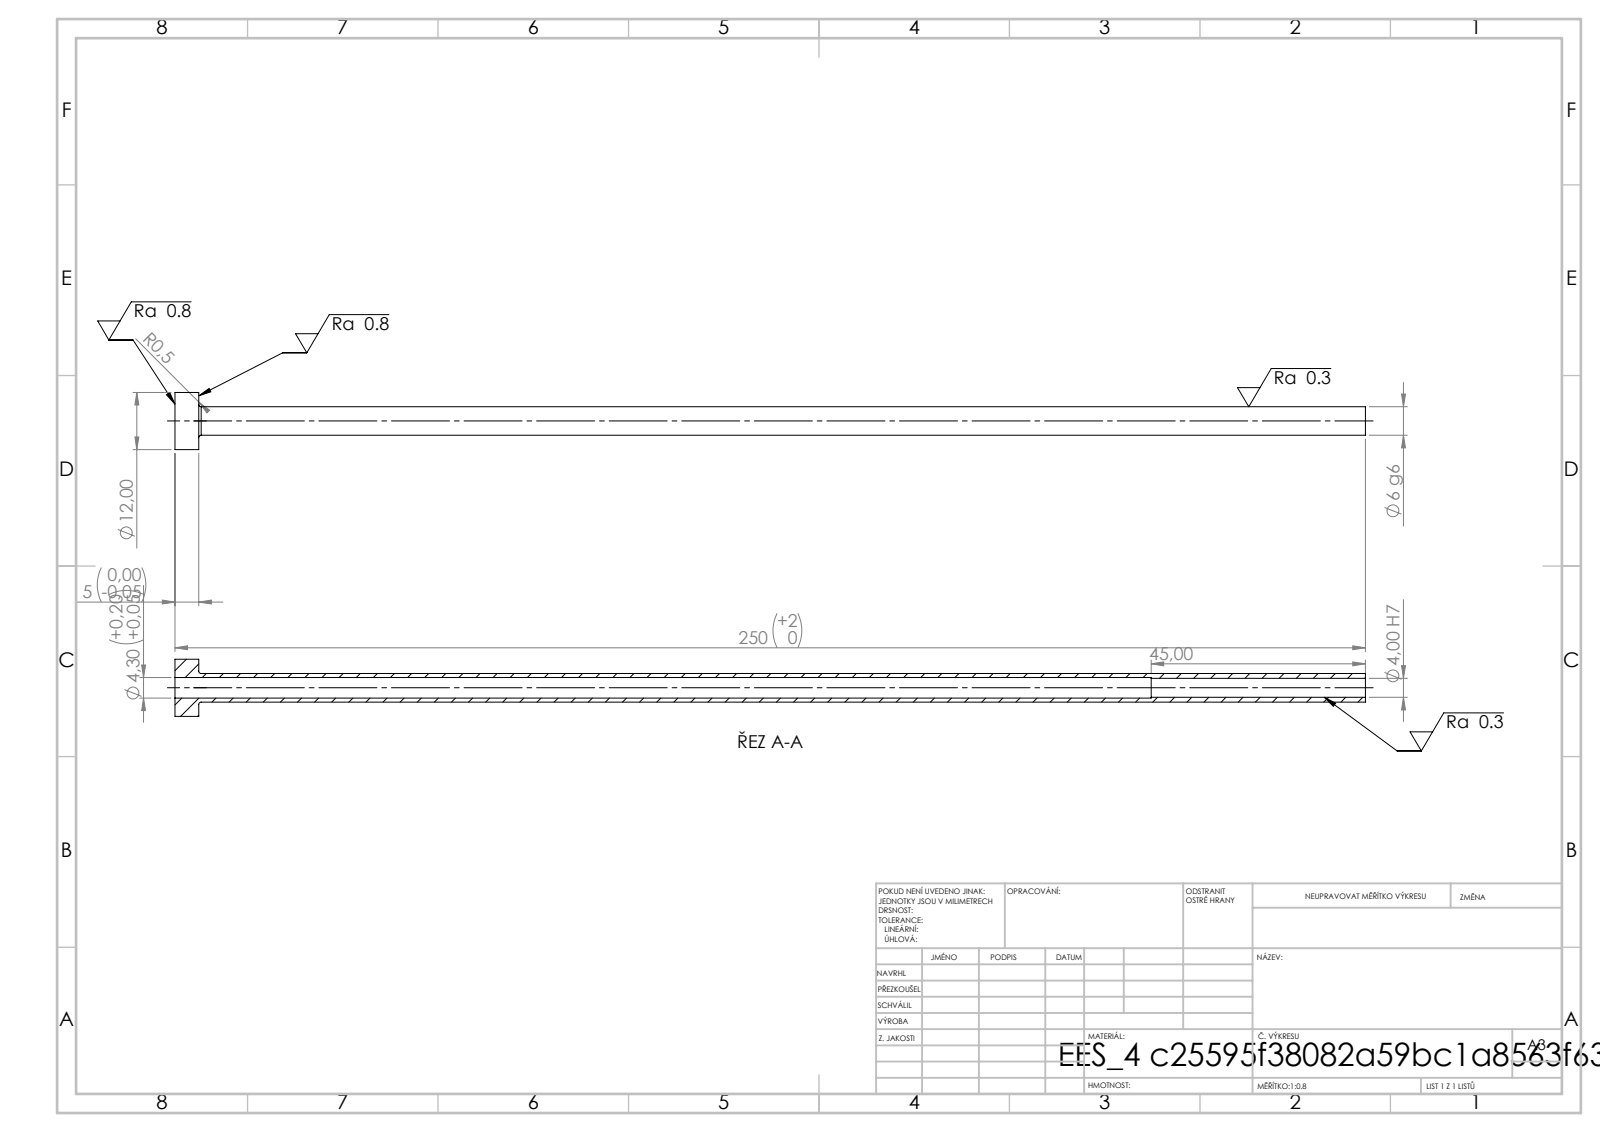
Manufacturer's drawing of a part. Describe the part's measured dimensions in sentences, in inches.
Its 3-D file was written by "SolidWorks 2019 (CONFIG_CONTROL_DESIGN)". It is 1 solid with 14 faces: 4 planar, 8 cylindrical and 2 other. Overall it measures 9.843 by 0.472 by 0.472 inches. Its volume is 0.241 cubic inches and its surface area 12.93 square inches. Round holes: 1 of diameter 0.157, 1 of diameter 0.169. Round bosses or shafts: 1 of diameter 0.472, 1 of diameter 0.236. The main face-to-face distances are 0.197, 9.843, 9.646, 8.071, 7.874, 1.772.
